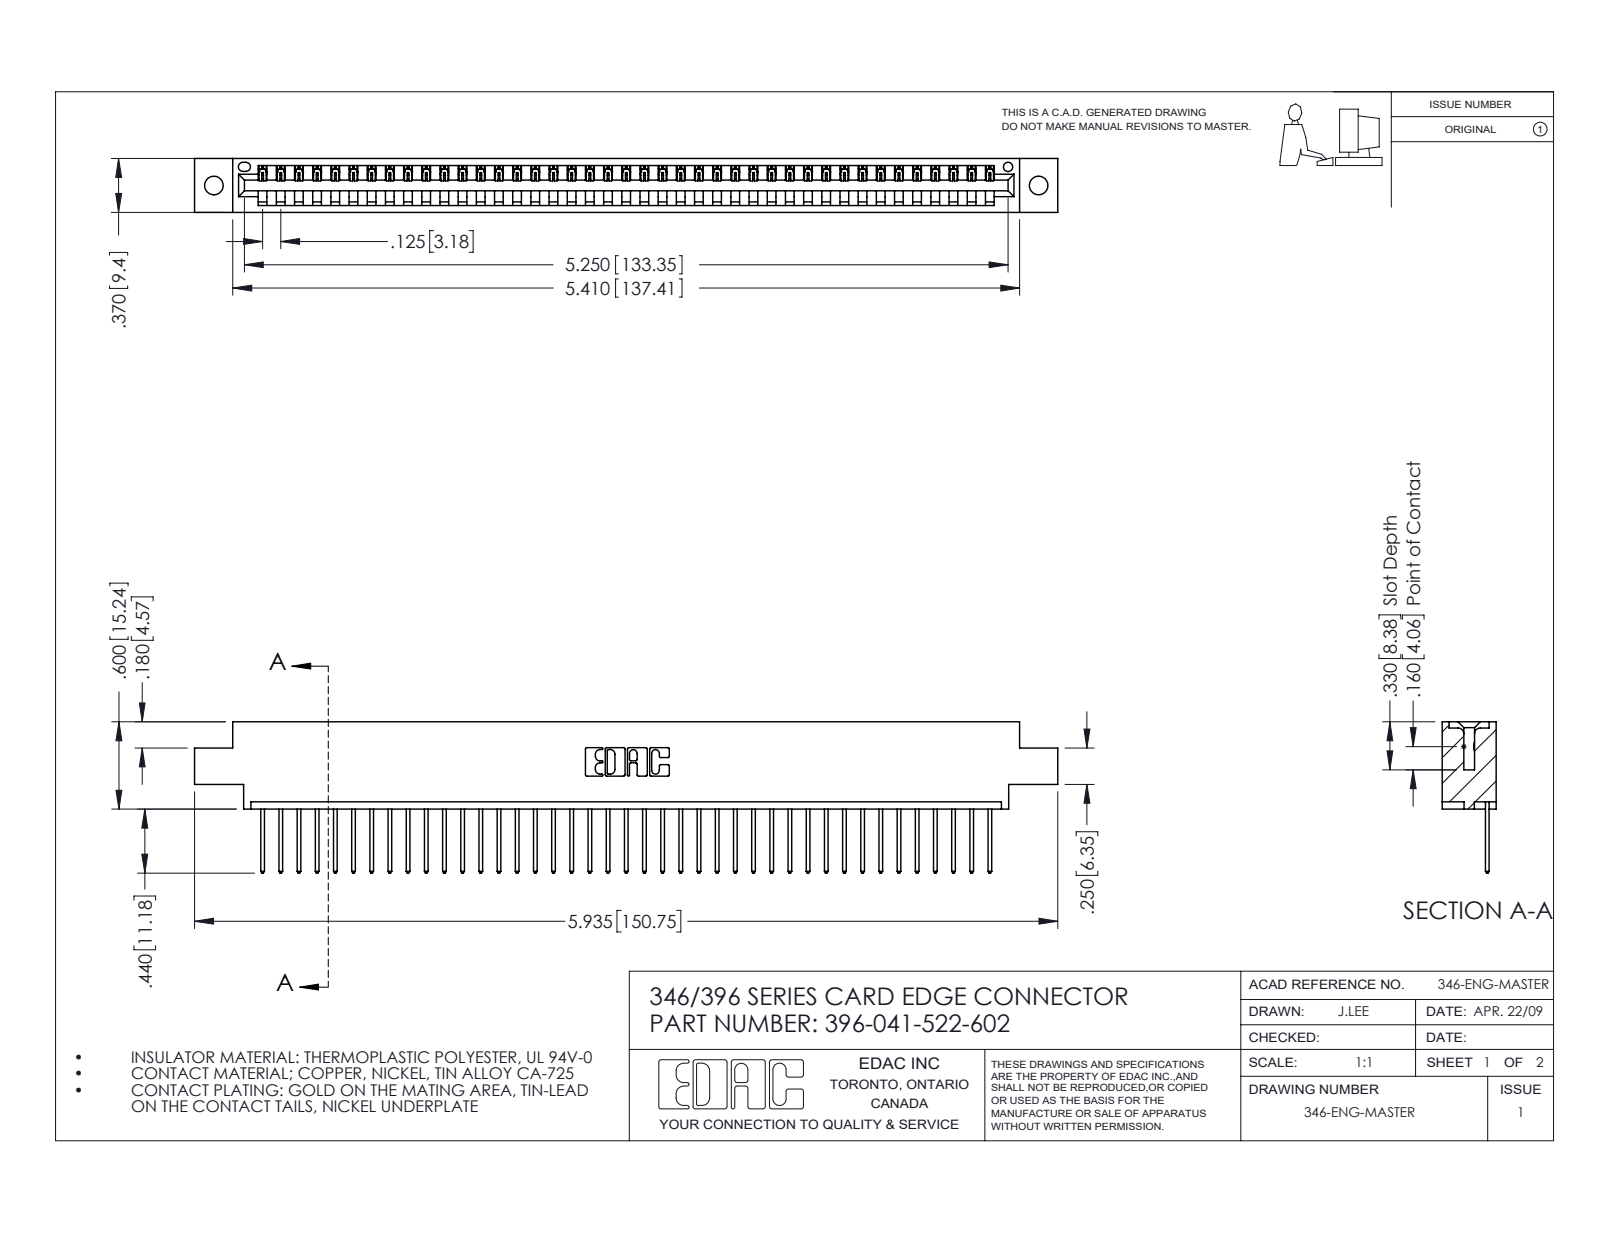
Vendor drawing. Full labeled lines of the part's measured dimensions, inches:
Part name (STEP PRODUCT): 396-041-522-602; 346 Part_0.170 Offset - 0.128 Dia; 345-292-001_345-293-122
STEP written by: SolidWorks 2016 (CONFIG_CONTROL_DESIGN)
Units: inches
Bodies: 42 solids, 2504 faces (1720 planar, 784 cylindrical, 0 other)
Overall size (bounding box): 5.935 × 1.04 × 0.37
Volume: 0.869 in³ · Surface area: 27.63 in²
Round holes (diameter × count): ⌀0.128 ×2, ⌀0.064 ×1
Partial cylindrical surfaces — rounded edges, fillets, slot ends (radius × count): R0.006 ×82, R0.01 ×82, R0.01 ×22, R0.007 ×6, R0.031 ×6, R0.026 ×3, R0.031 ×2, R0.04 ×2
Main face-to-face distances: 0.048, 0.322, 0.37, 0.25, 0.072, 0.298, 0.025, 0.148, 0.222, 0.1
Hole centre spacings: 0.246, 5.461, 5.67
